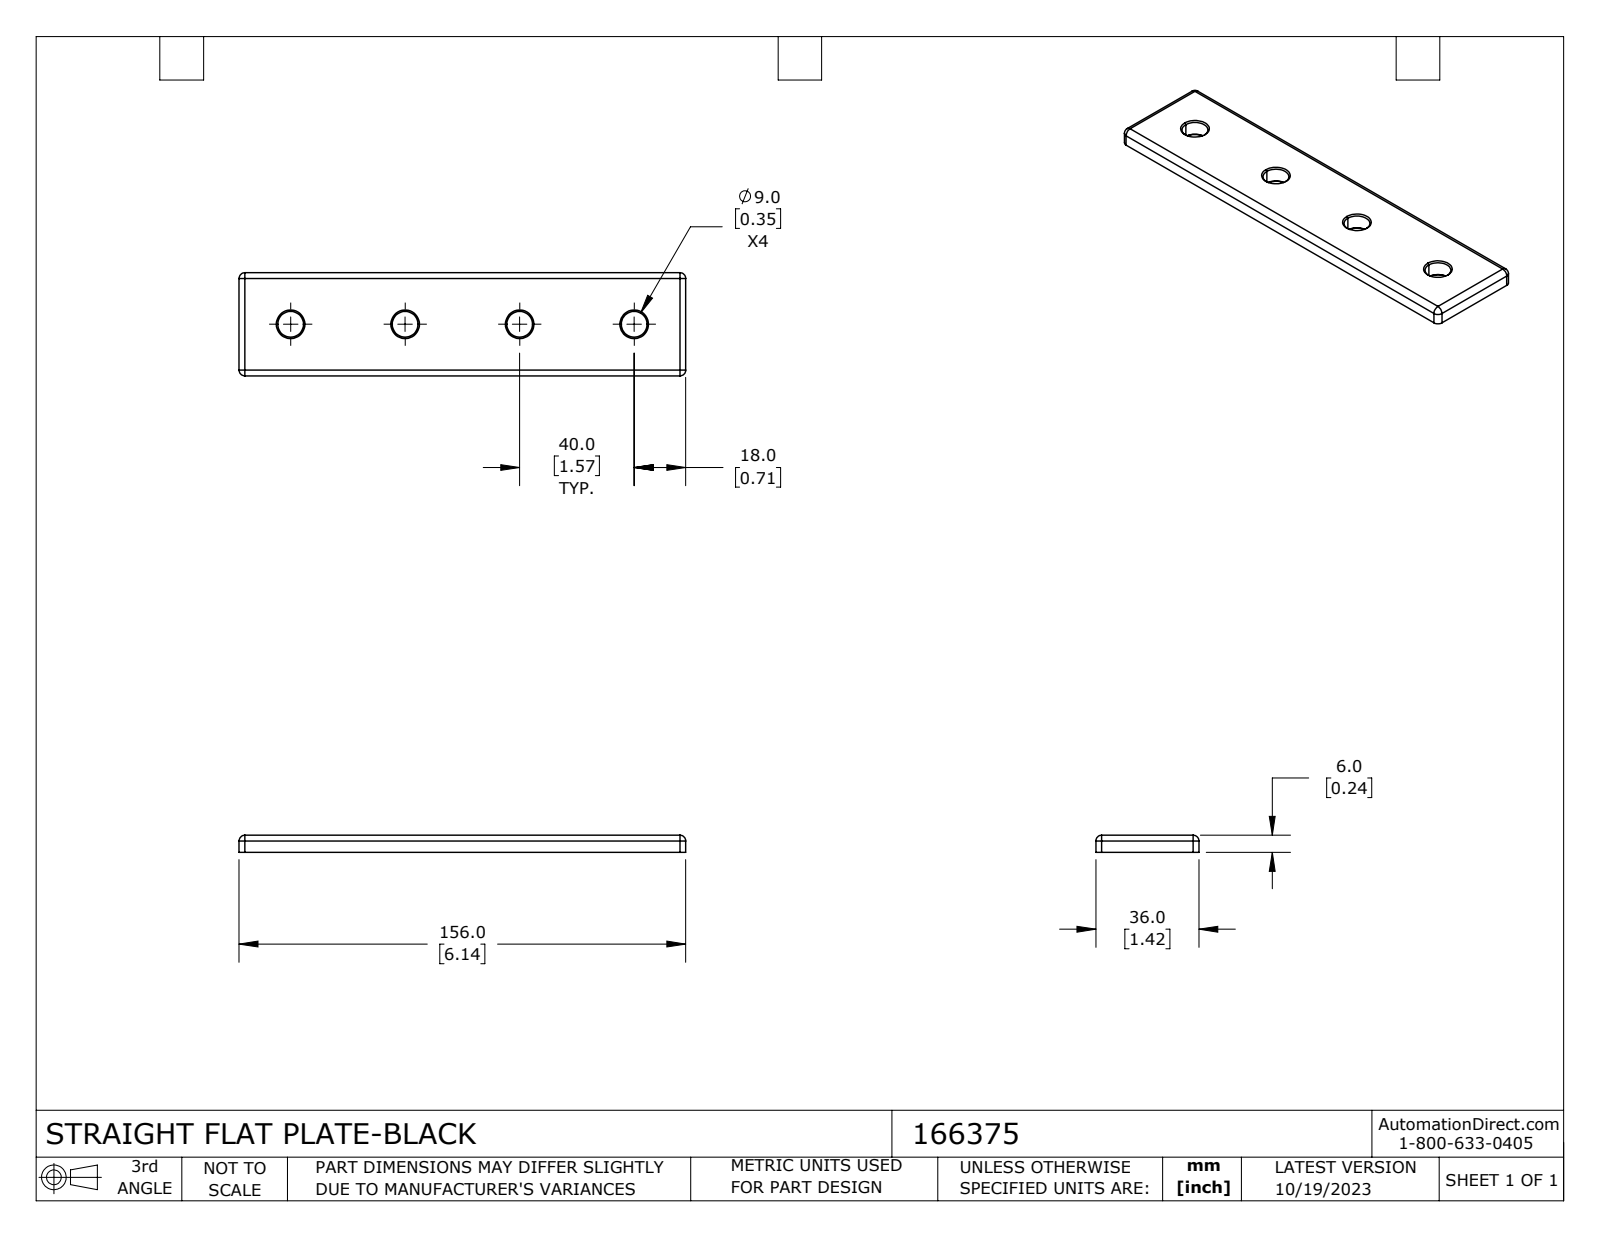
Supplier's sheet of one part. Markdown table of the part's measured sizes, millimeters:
| quantity | value |
| --- | --- |
| part name | 166375 |
| STEP written by | SolidWorks 2023 (CONFIG_CONTROL_DESIGN) |
| units | millimeters |
| bodies | 1 solid, 42 faces (6 planar, 16 cylindrical, 20 other) |
| overall size | 156 × 36 × 6 |
| volume | 31 795 mm³ |
| surface area | 13 286 mm² |
| round holes (diameter × count) | 9 × 4 |
| partial cylindrical surfaces (radius × count) | 2 × 8 |
| main face-to-face distances | 6, 36, 156 |
| hole center spacings | 40, 80, 120 |
